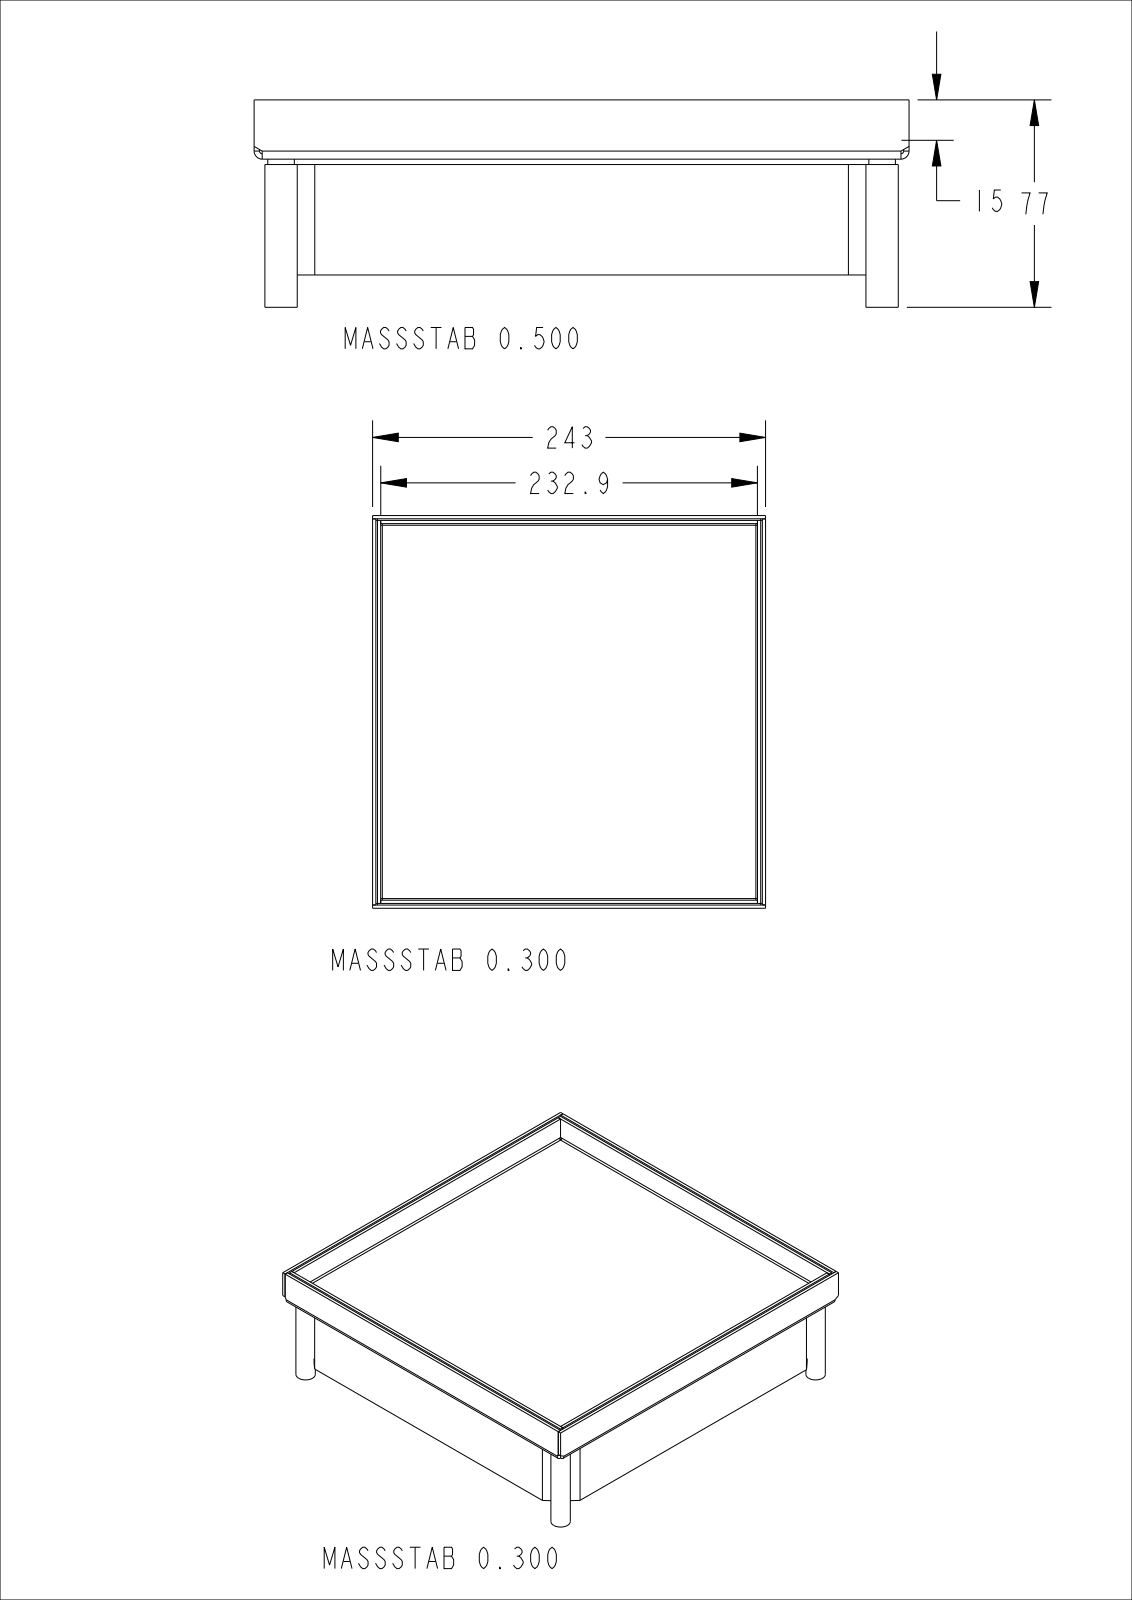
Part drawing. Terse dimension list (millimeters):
name: T-00626_1; T-00632_1; T-00625_1; T-00823_ASM_1_ASM (+4 more)
written by: CREO PARAMETRIC BY PTC INC, 2022281 (AUTOMOTIVE_DESIGN)
unit: mm
bodies: 7 solids, 166 faces (110 planar, 56 cylindrical, 0 other)
size: 243 × 243 × 77
volume: 295 628 mm³; area: 290 385 mm²
holes: 4× ⌀6.8, 4× ⌀8.5
bosses: 4× ⌀12, 4× ⌀9.85
rounds: 8× R1, 8× R3, 1× R150, 1× R152.5
face distances: 2, 3, 2.5, 235, 5, 238, 229.5, 232, 1, 6
hole spacings: 223, 315.37
